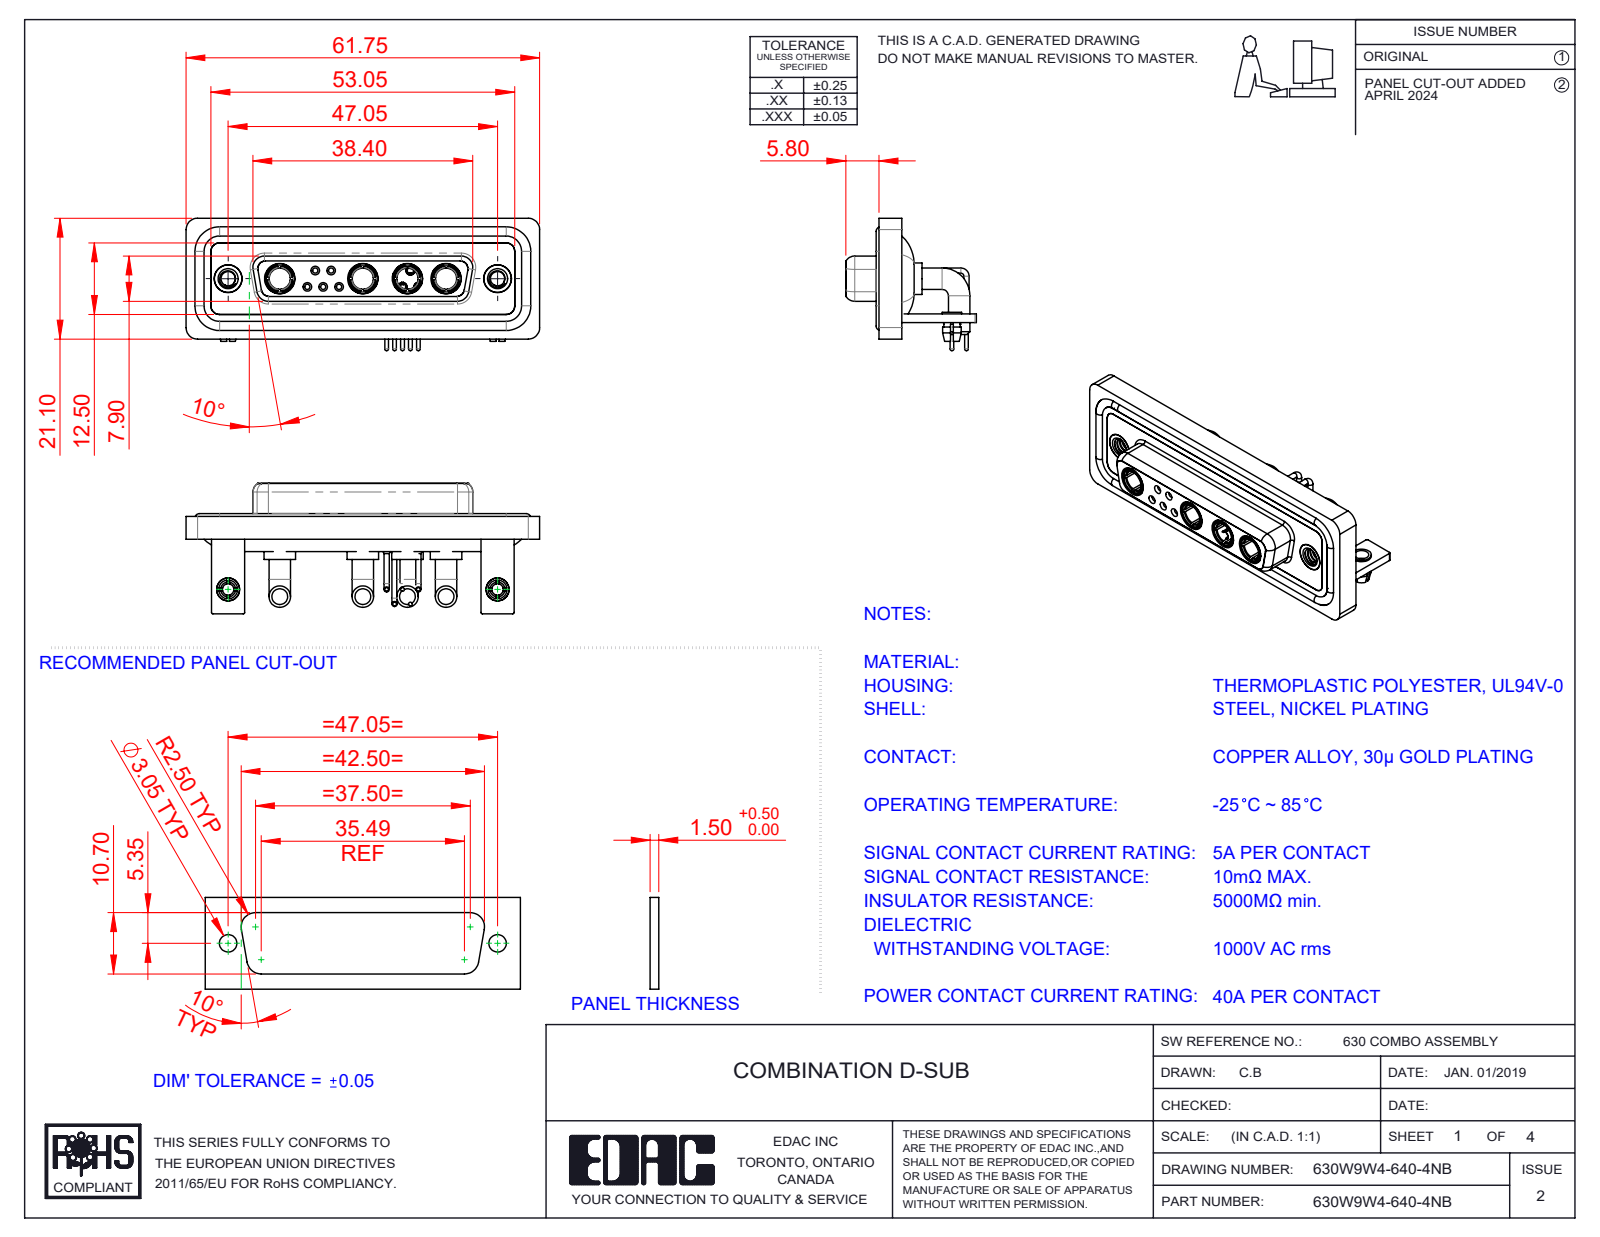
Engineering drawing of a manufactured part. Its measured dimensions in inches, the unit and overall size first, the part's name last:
Units: inches
Overall size (bounding box): 2.431 × 0.91 × 0.898
Round holes (diameter × count): ⌀0.079 ×7, ⌀0.191 ×6, ⌀0.035 ×5, ⌀0.043 ×5, ⌀0.059 ×5, ⌀0.098 ×4, ⌀0.146 ×4, ⌀0.209 ×4, ⌀0.063 ×3, ⌀0.067 ×2, ⌀0.126 ×2, ⌀0.157 ×2
Round bosses / shafts (diameter × count): ⌀0.035 ×10, ⌀0.063 ×9, ⌀0.148 ×8, ⌀0.079 ×5, ⌀0.059 ×5, ⌀0.026 ×5, ⌀0.217 ×4, ⌀0.205 ×4
Partial cylindrical surfaces — rounded edges, fillets, slot ends (radius × count): R0.079 ×19, R0.059 ×18, R0.01 ×16, R0.053 ×8, R0.063 ×8, R0.02 ×5, R0.024 ×4, R0.026 ×4
Main face-to-face distances: 0.016, 0.071, 0.114, 0.146, 0.059, 0.161, 0.043, 0.055, 0.063, 0.098
Hole centre spacings: 0.124, 0.109, 0.198, 0.545, 0.436, 0.504, 0.61, 0.218
Volume: 0.558 in³ · Surface area: 23.52 in²
Bodies: 24 solids, 1097 faces (364 planar, 457 cylindrical, 276 other)
Part name (STEP PRODUCT): 630Combo Shell Rear_25 Contacts; 630Combo Housing_9W4; 630Combo Board Lock_50 Contacts; 630W9W4-640-4NB (+7 more)
STEP written by: SolidWorks 2023 (CONFIG_CONTROL_DESIGN)
